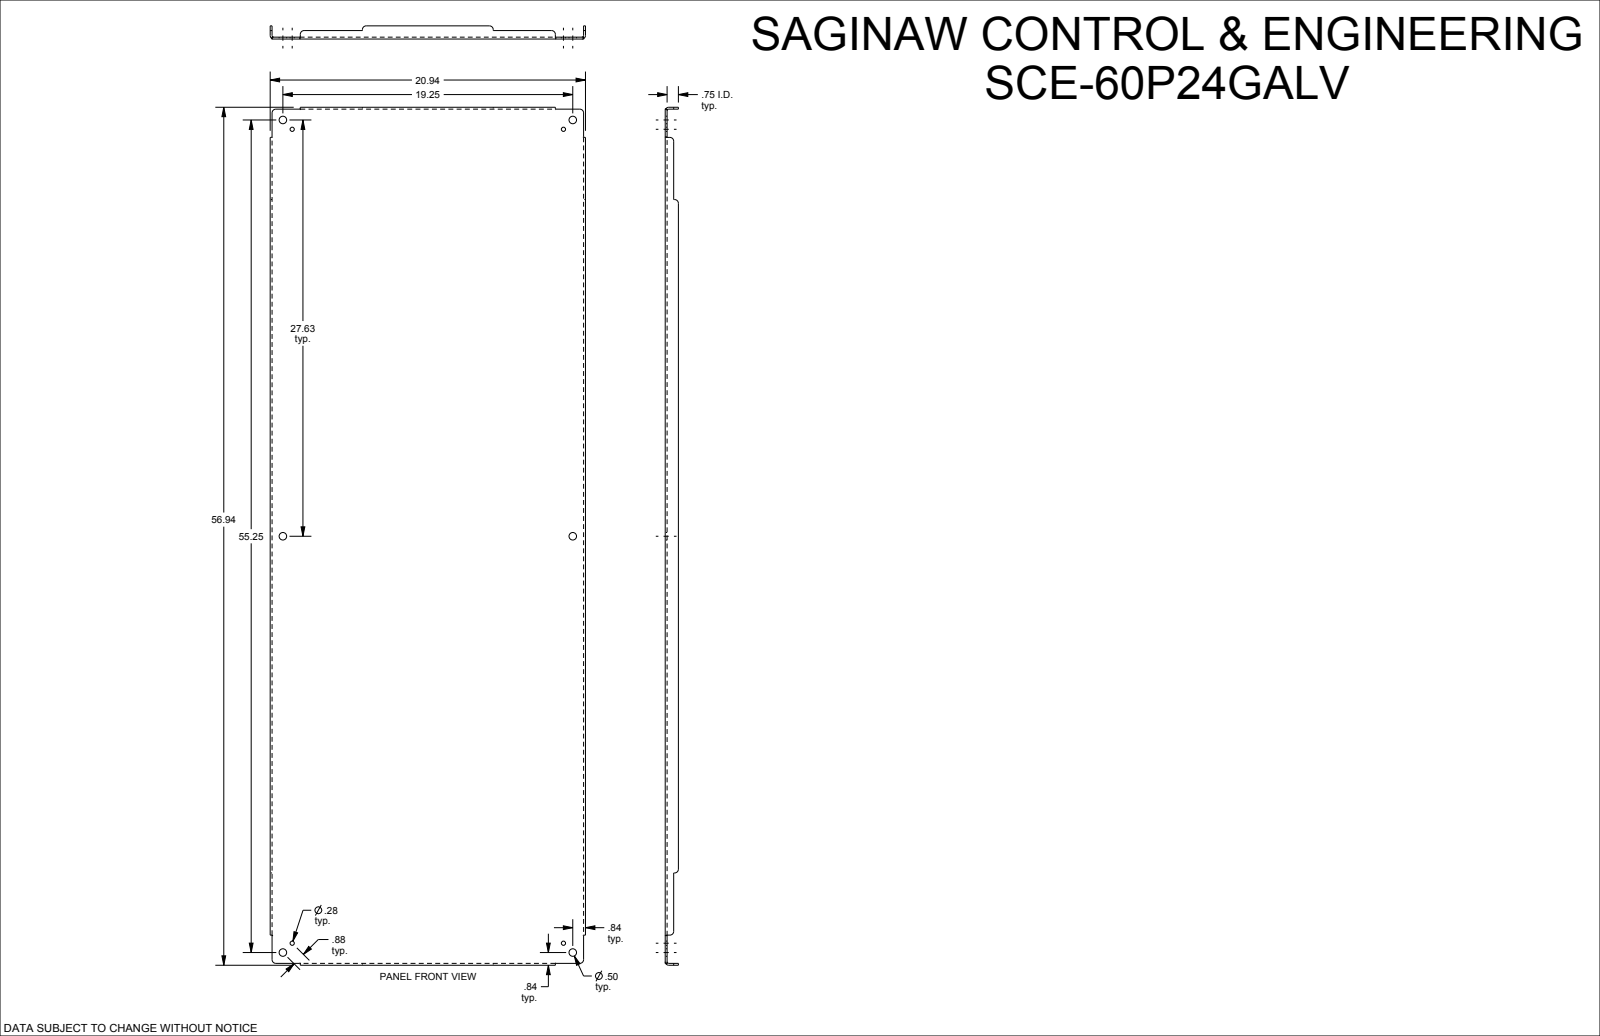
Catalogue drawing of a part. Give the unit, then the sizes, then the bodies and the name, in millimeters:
Units: millimetres
Overall size (bounding box): 1446.2 × 531.8 × 22.2
Round holes (diameter × count): ⌀12.7 ×6, ⌀7.1 ×4
Partial cylindrical surfaces — rounded edges, fillets, slot ends (radius × count): R6.4 ×12, R2.8 ×4, R6 ×4
Main face-to-face distances: 3.2, 3.2, 528.7, 525.4, 531.8, 1443.1, 19.1, 22.2, 1439.8, 1446.2
Hole centre spacings: 22.2, 473.5, 686.1, 701.7, 833.3, 855.2, 1387.7, 1466.1
Volume: 2 607 000 mm³ · Surface area: 1 656 000 mm²
Bodies: 1 solid, 108 faces (46 planar, 38 cylindrical, 24 other)
Part name (STEP PRODUCT): SCE-60P24GALV
STEP written by: SolidWorks 2019 (CONFIG_CONTROL_DESIGN)
